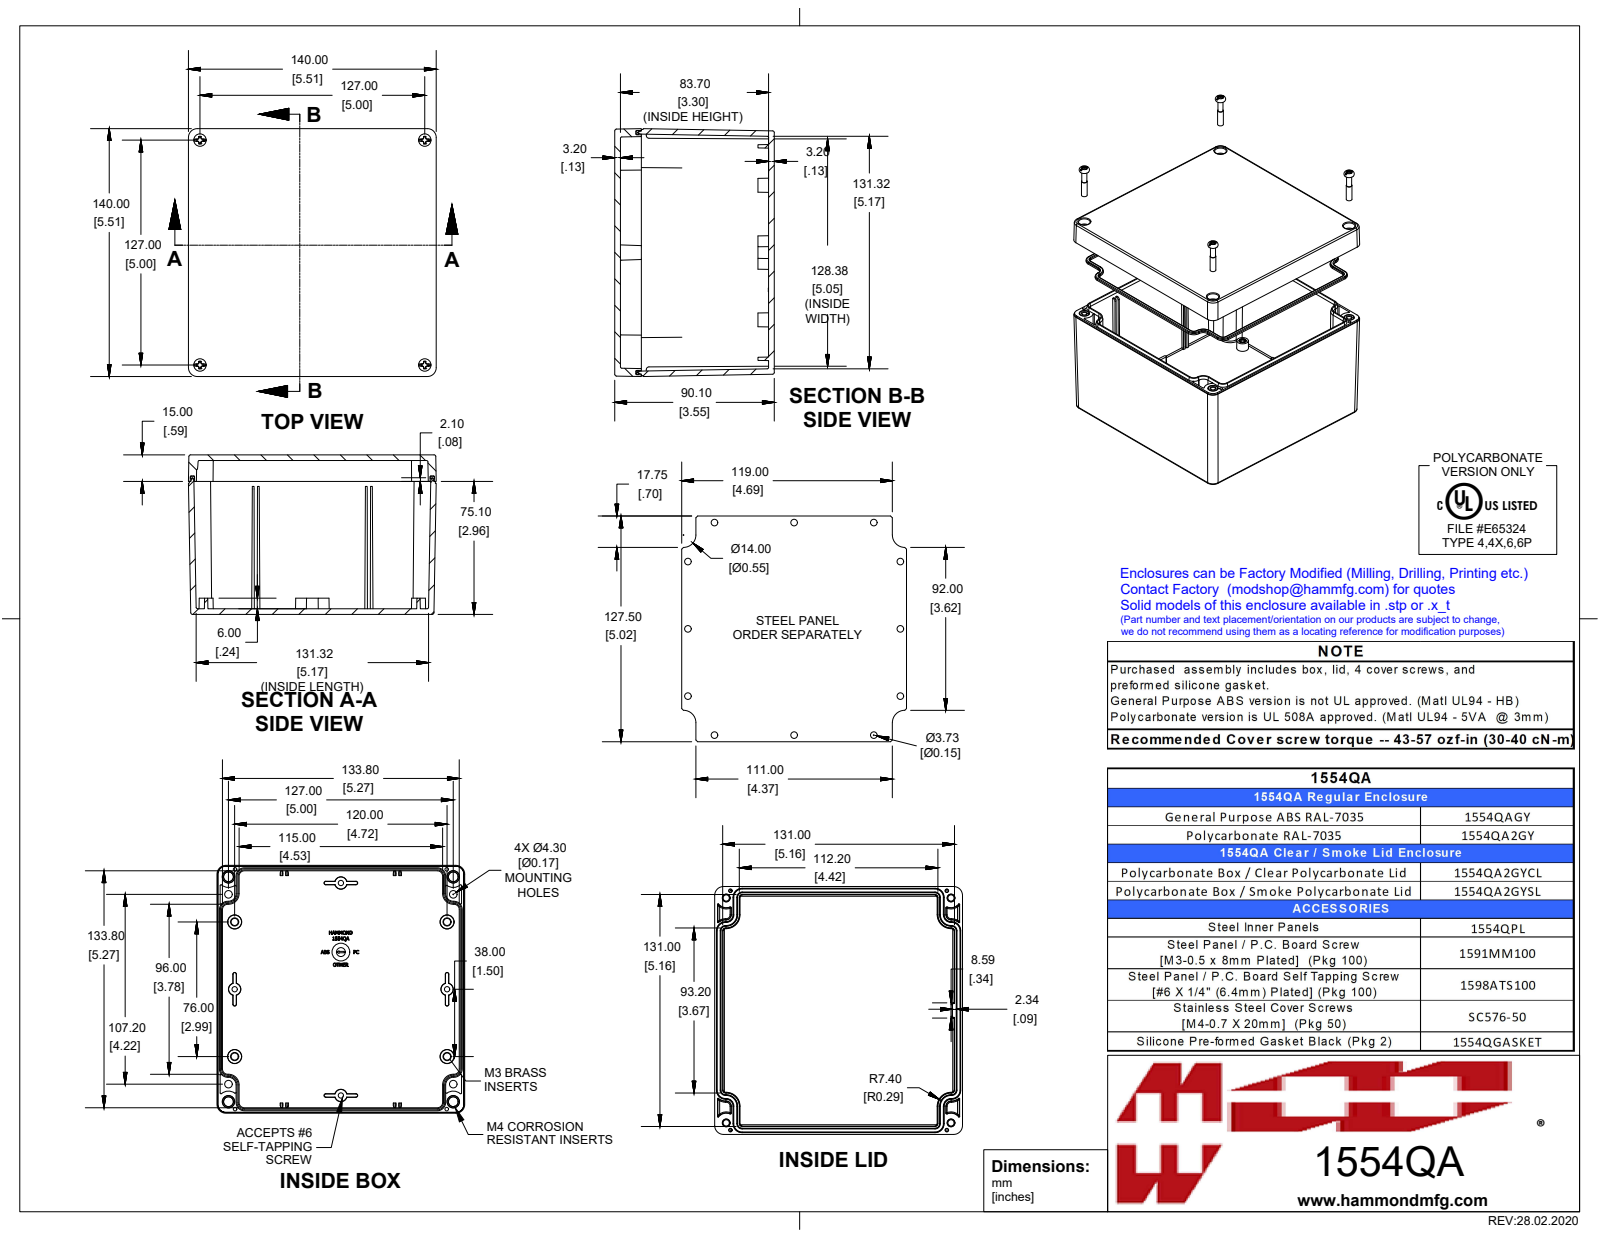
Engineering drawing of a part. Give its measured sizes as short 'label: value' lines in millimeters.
name: 1554QAGY
written by: SolidWorks 2019 (AUTOMOTIVE_DESIGN)
unit: mm
bodies: 15 solids, 1876 faces (623 planar, 374 cylindrical, 879 other)
size: 140 × 140 × 90.1
volume: 297 100 mm³; area: 201 500 mm²
holes: 4× ⌀2.5, 4× ⌀3.3, 4× ⌀4.6
bosses: 4× ⌀6.4, 4× ⌀5.5, 4× ⌀5.3, 4× ⌀4.8, 4× ⌀3.9, 4× ⌀3.9, 4× ⌀3.8, 4× ⌀3.4
rounds: 26× R0.5, 20× R0.3, 12× R1, 10× R0.8, 8× R2.6, 8× R5, 8× R5.1, 4× R3
face distances: 3.2, 86.9, 3.1, 90.1, 83.7, 140, 136.9, 135.5, 132.4, 4.5
hole spacings: 25.7, 101.5, 126.1, 127, 159.9, 76, 120, 142
